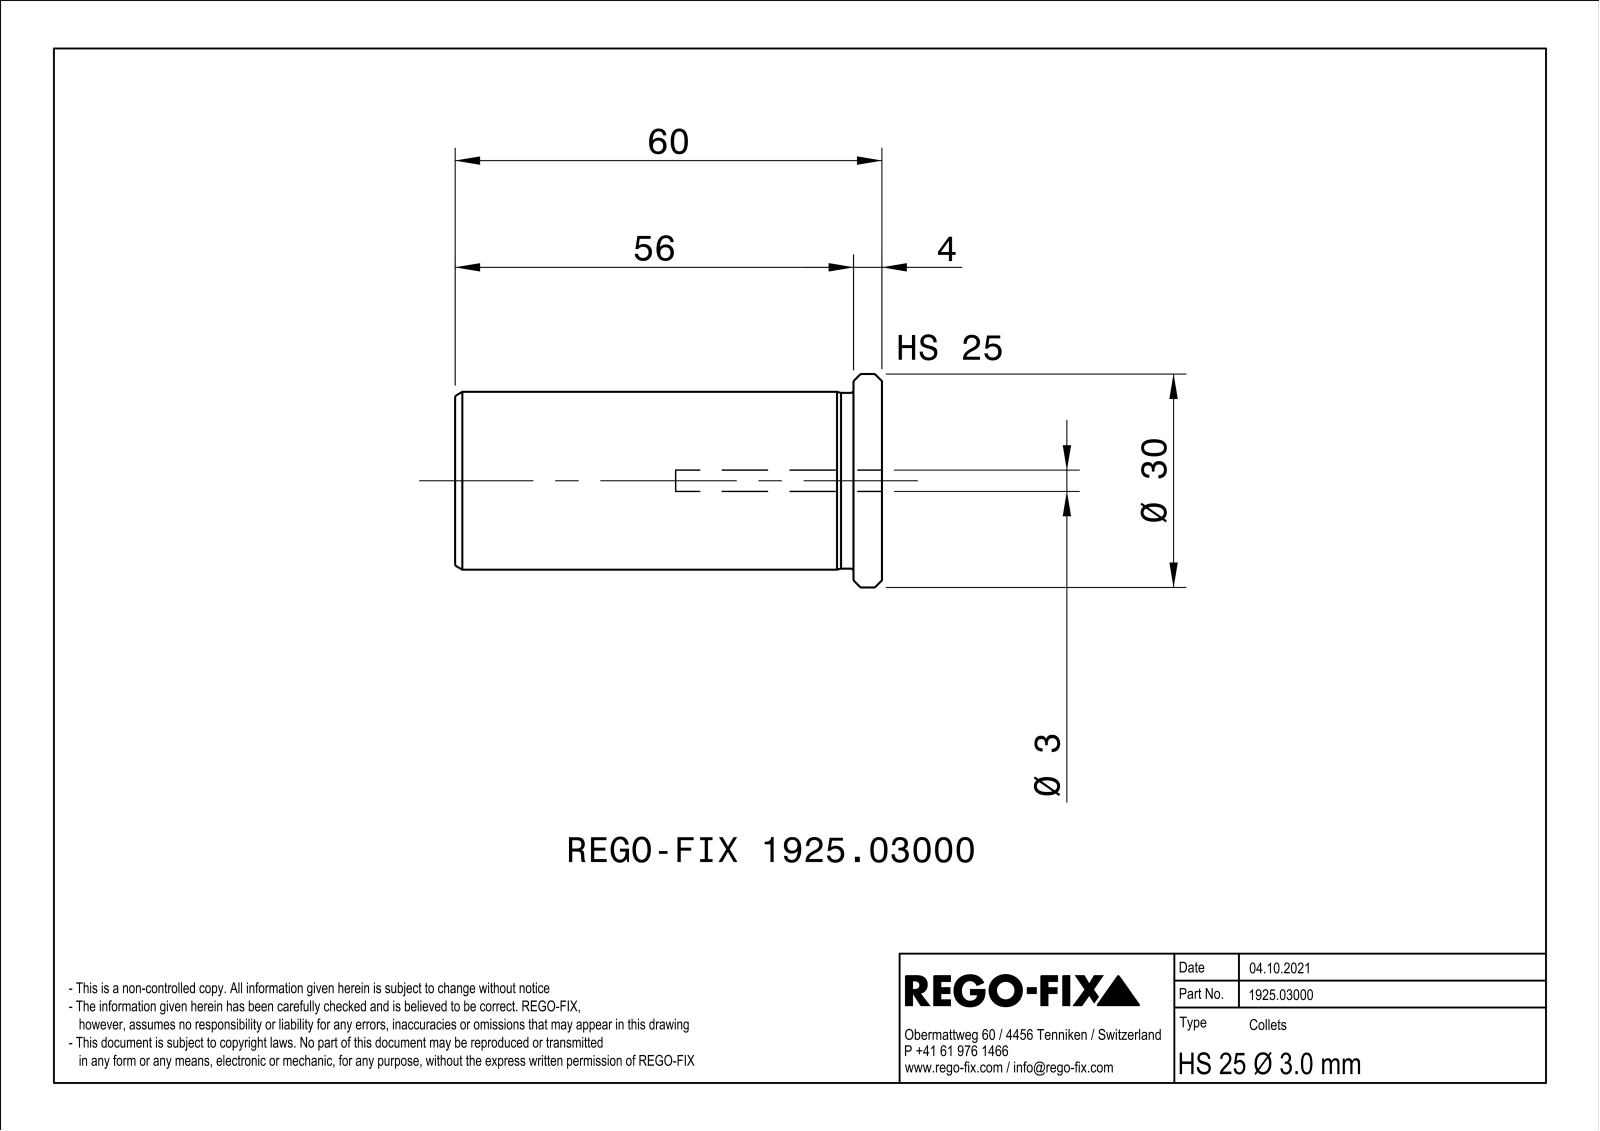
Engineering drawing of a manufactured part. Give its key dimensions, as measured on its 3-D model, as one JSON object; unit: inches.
{"part_name": "NOCUT", "step_written_by": "SIEMENS PLM Software Solid Edge ST10 (AUTOMOTIVE_DESIGN)", "units": "inches", "bodies": {"solids": 1, "faces": 177, "planar": 96, "cylindrical": 12, "other": 69}, "overall_size": [2.362, 1.18, 1.18], "volume_in3": 1.409, "surface_area_in2": 15.71, "round_holes": [[0.157, 1], [0.394, 1], [0.807, 1]], "round_bosses_or_shafts": [[1.181, 1], [0.984, 1], [0.972, 1]], "face_to_face_distances": [0.039, 0.157, 2.362, 2.205, 0.156, 2.36, 0.059, 0.049, 0.05, 0.073]}
